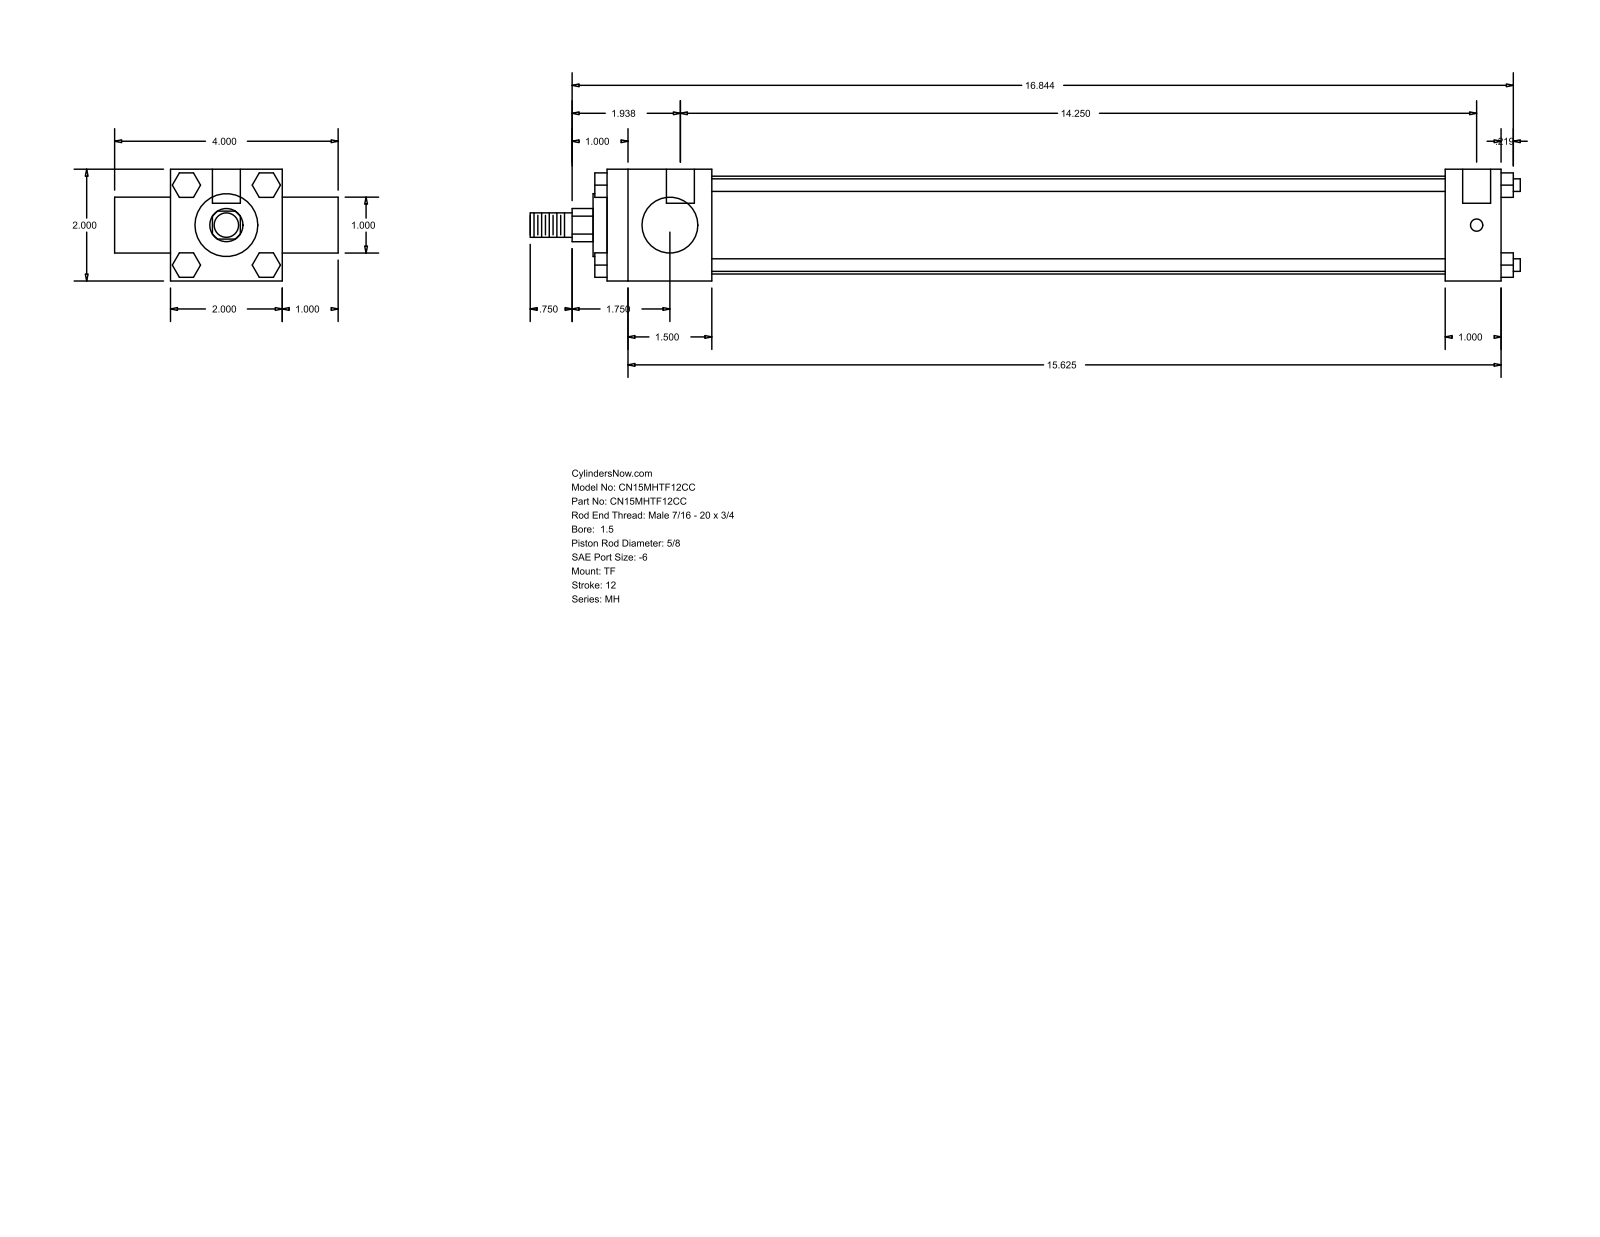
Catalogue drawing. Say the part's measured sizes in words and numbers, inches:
The part is named "MH_TF__0150_0.625". Its 3-D file was written by "GSSL Pune (CONFIG_CONTROL_DESIGN)". It is 0 solids with 120 faces: 92 planar, 28 cylindrical and 0 other. Overall it measures 17.719 by 4 by 2 inches. Round holes: 3 of diameter 0.219, 2 of diameter 0.5. Round bosses or shafts: 4 of diameter 0.225, 1 of diameter 1.75, 1 of diameter 1.125, 1 of diameter 1, 1 of diameter 0.625, 1 of diameter 0.437. Partial cylindrical surfaces (rounded edges, fillets, slot ends): 1 of radius 0.297. The main face-to-face distances are 2, 16, 1, 3, 1.875, 14.125, 15, 13.125, 1, 0.219. The hole center spacings are 0.125, 14.25, 14.375.
